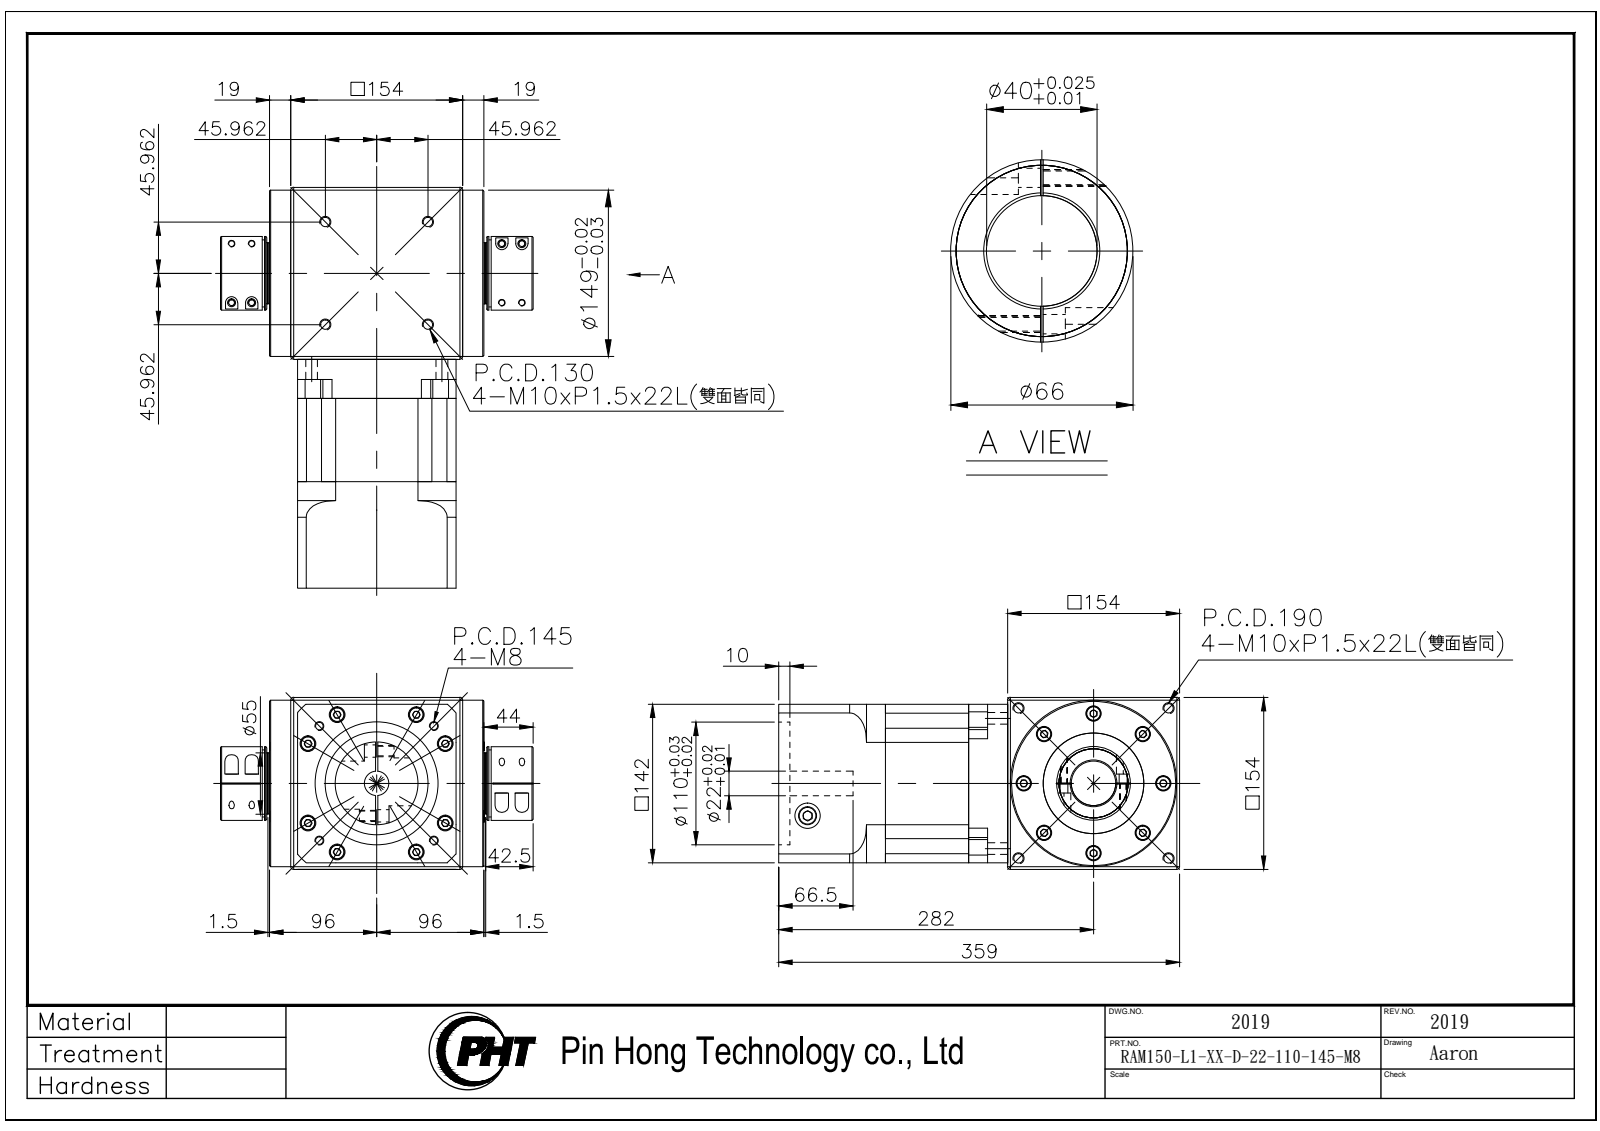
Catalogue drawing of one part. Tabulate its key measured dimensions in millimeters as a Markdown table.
| quantity | value |
| --- | --- |
| part name | RAM150-L1-XX-D-22-110-145-M8_2019 |
| STEP written by | SolidWorks 2016 (AUTOMOTIVE_DESIGN) |
| units | millimeters |
| bodies | 4 solids, 1251 faces (625 planar, 408 cylindrical, 218 other) |
| overall size | 359 × 280 × 154 |
| volume | 7 688 000 mm³ |
| surface area | 578 302 mm² |
| round holes (diameter × count) | 8.5 × 12, 9 × 8, 11 × 8, 14 × 8, 17.5 × 8, 7 × 6, 6.8 × 4, 10.5 × 4, 22.5 × 2, 22 × 1, 40 × 1, 44 × 1 |
| round bosses / shafts (diameter × count) | 16 × 12, 13 × 8, 10.5 × 8, 10 × 8, 6 × 8, 149 × 1, 130 × 1, 90 × 1 |
| partial cylindrical surfaces (radius × count) | 3.52 × 8, 5.5 × 8, 10 × 4, 80 × 1, 95 × 1, 107.4 × 1 |
| main face-to-face distances | 6, 148, 154, 142, 74.5, 35, 109.5, 263.5, 189, 167 |
| hole center spacings | 71, 18.72, 18.79, 23.06, 47.83, 67.34, 82.93, 87.37 |
